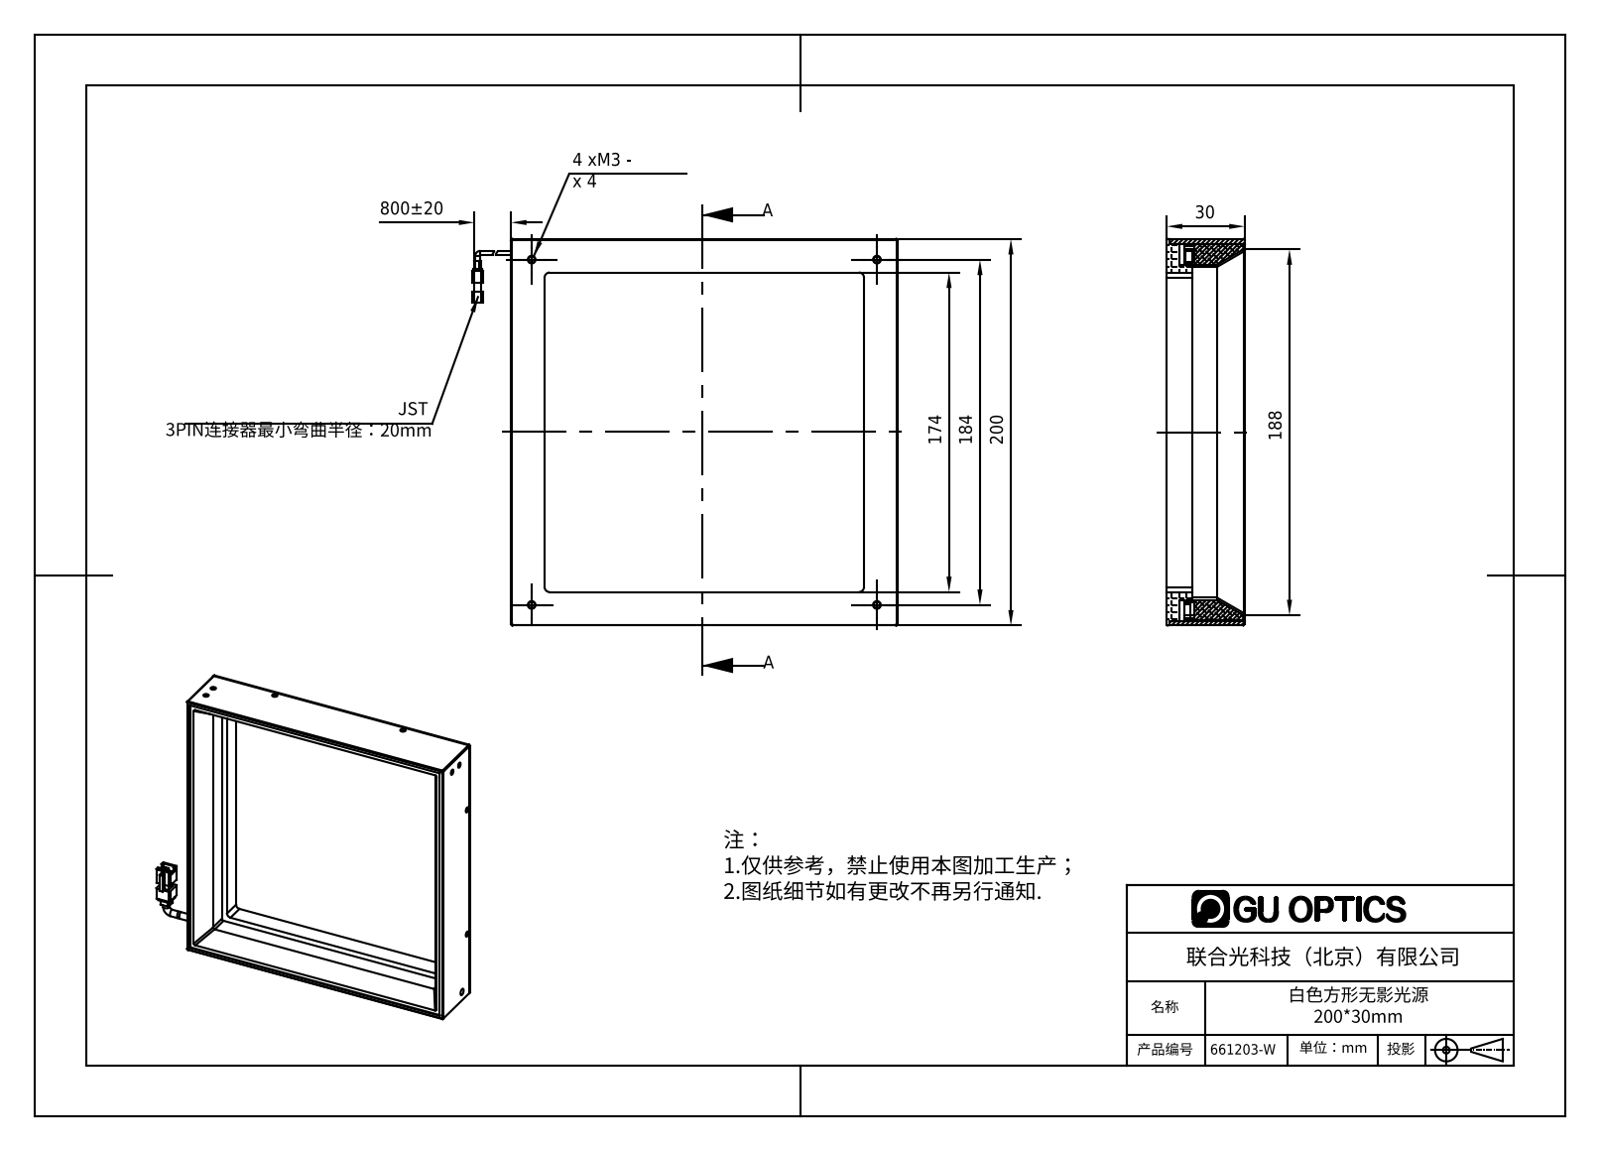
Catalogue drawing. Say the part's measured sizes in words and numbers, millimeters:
The part is named "661203-W". Its 3-D file was written by "SolidWorks 2016 (AUTOMOTIVE_DESIGN)". It is 5 solids with 512 faces: 228 planar, 183 cylindrical and 101 other. Overall it measures 177 by 150 by 30.2 millimeters. Its volume is 141 726 cubic millimeters and its surface area 99 470 square millimeters. Round holes: 12 of diameter 1.25, 12 of diameter 1.5, 12 of diameter 1.6, 12 of diameter 2.8, 4 of diameter 2.5, 4 of diameter 3. Round bosses or shafts: 2 of diameter 3.5. Partial cylindrical surfaces (rounded edges, fillets, slot ends): 15 of radius 1, 8 of radius 0.5, 4 of radius 2. The main face-to-face distances are 1.8, 148.2, 2, 148, 146.2, 146.4, 138.1, 150, 146, 9.9. The hole center spacings are 8, 32.63, 35.56, 106.84, 107.77, 134, 138, 138.23.
